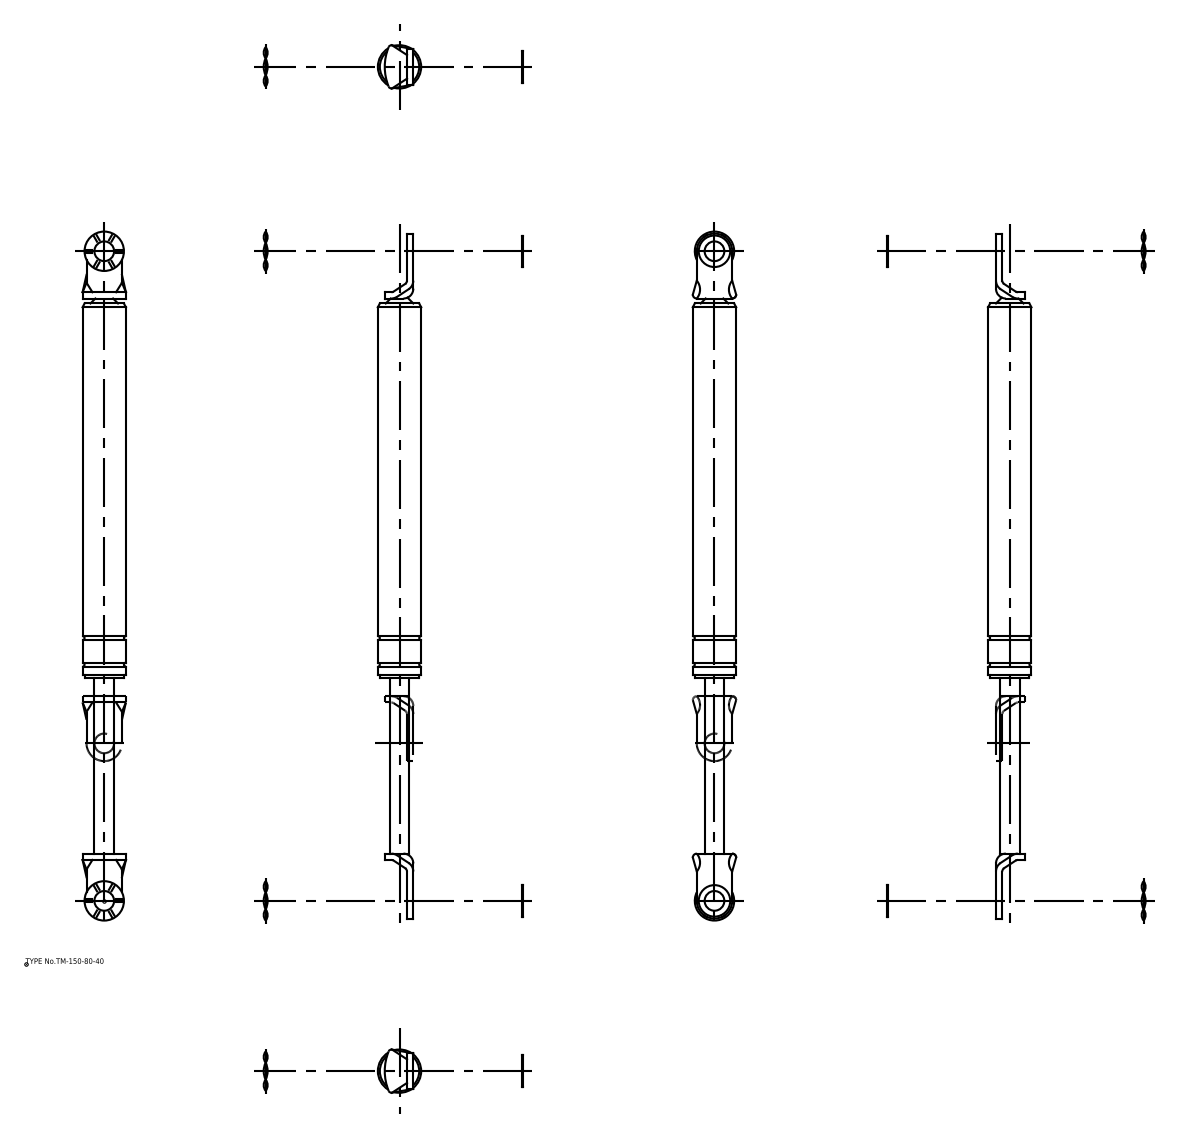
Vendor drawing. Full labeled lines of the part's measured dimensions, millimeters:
Part name (STEP PRODUCT): ウェーブワッシャー; ワッシャー; 本体; 本体_div
STEP written by: spGate 16.7.1 (AUTOMOTIVE_DESIGN)
Units: millimetres
Bodies: 6 solids, 94 faces (42 planar, 44 cylindrical, 8 other)
Overall size (bounding box): 350 × 22.5 × 22.5
Volume: 85 116 mm³ · Surface area: 22 418 mm²
Round holes (diameter × count): ⌀10 ×2
Round bosses / shafts (diameter × count): ⌀20 ×3, ⌀16 ×2, ⌀22.5 ×1, ⌀22 ×1, ⌀10 ×1
Partial cylindrical surfaces — rounded edges, fillets, slot ends (radius × count): R4.4 ×2, R5 ×2, R9 ×2, R26.32 ×1
Main face-to-face distances: 3.2, 2, 5.2, 285.2, 5.7, 3.7, 0.5, 196.2, 92.2, 288.4
Hole centre spacings: 330
